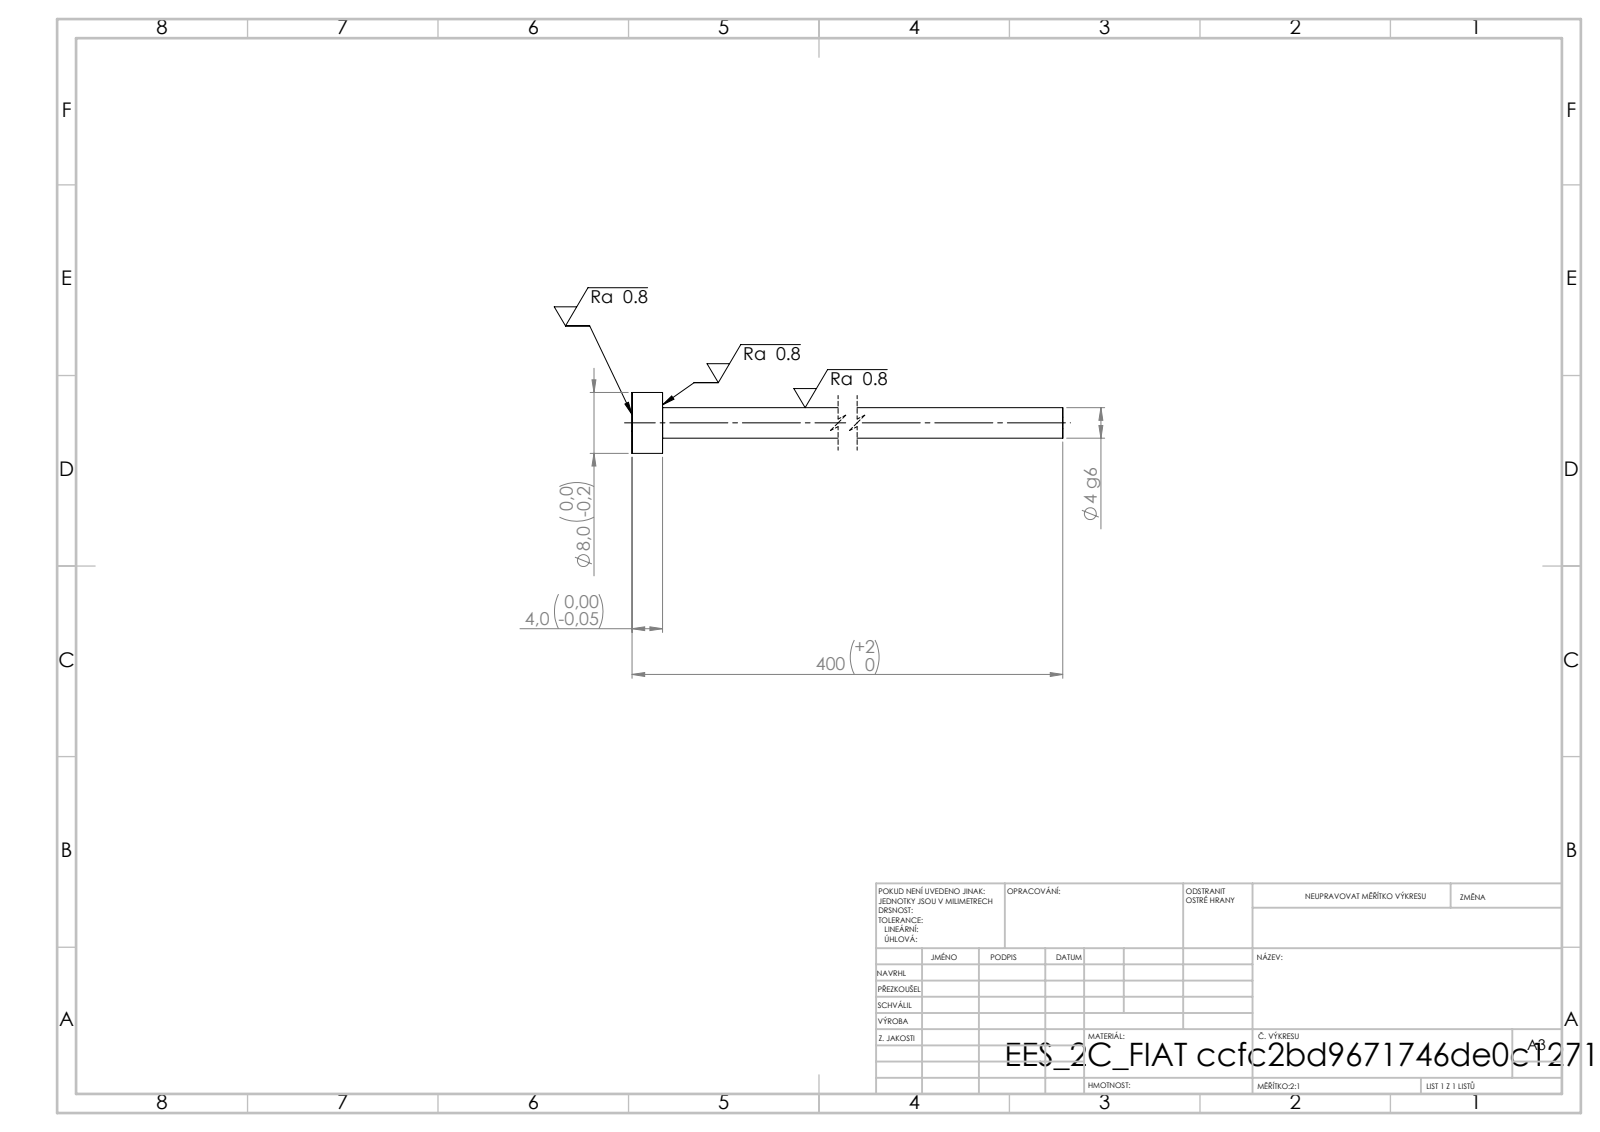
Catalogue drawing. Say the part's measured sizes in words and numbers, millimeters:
Its 3-D file was written by "SolidWorks 2019 (CONFIG_CONTROL_DESIGN)". It is 1 solid with 7 faces: 3 planar, 4 cylindrical and 0 other. Overall it measures 400 by 8 by 8 millimeters. Its volume is 5 177 cubic millimeters and its surface area 5 177 square millimeters. Round bosses or shafts: 1 of diameter 8, 1 of diameter 4. The main face-to-face distances are 4, 400, 396.
